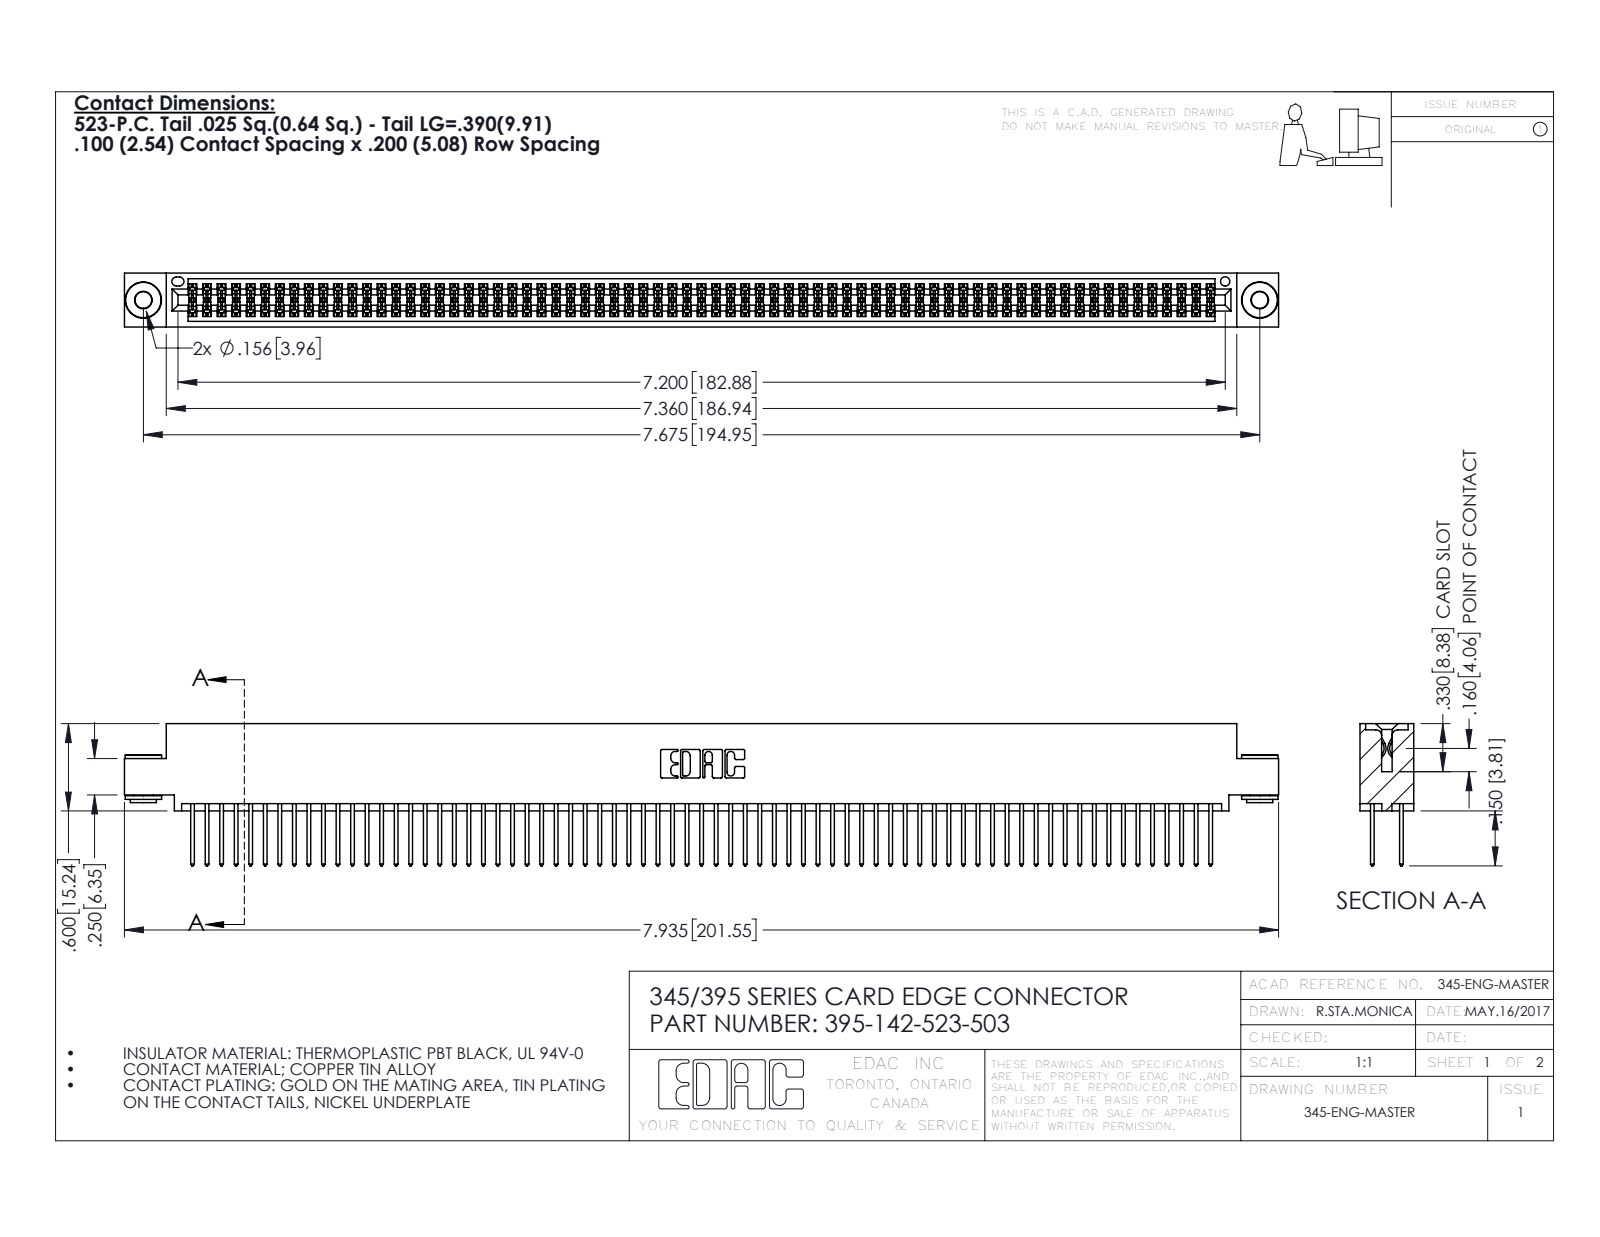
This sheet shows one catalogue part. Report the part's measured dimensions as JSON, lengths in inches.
{"part_name": "345-250-002_345-250-002-102; 345-292-001_345-293-123; 345 Part_0.110 Offset - 0.156 Dia-TH; 395-142-523-503", "step_written_by": "SolidWorks 2016 (CONFIG_CONTROL_DESIGN)", "units": "inches", "bodies": {"solids": 145, "faces": 7268, "planar": 4780, "cylindrical": 2480, "other": 8}, "overall_size": [7.935, 0.977, 0.37], "volume_in3": 1.226, "surface_area_in2": 49.37, "round_holes": [[0.116, 2], [0.156, 2], [0.064, 1]], "round_bosses_or_shafts": [[0.25, 2], [0.18, 2], [0.136, 2]], "partial_cylinders_radius": [[0.006, 213], [0.01, 142], [0.01, 22], [0.007, 6], [0.031, 6], [0.026, 3], [0.014, 2], [0.019, 2]], "face_to_face_distances": [0.072, 0.298, 0.2, 0.025, 0.098, 0.272, 0.37, 0.225, 0.175, 0.149], "hole_center_spacings": [0.27, 7.439, 7.675]}
